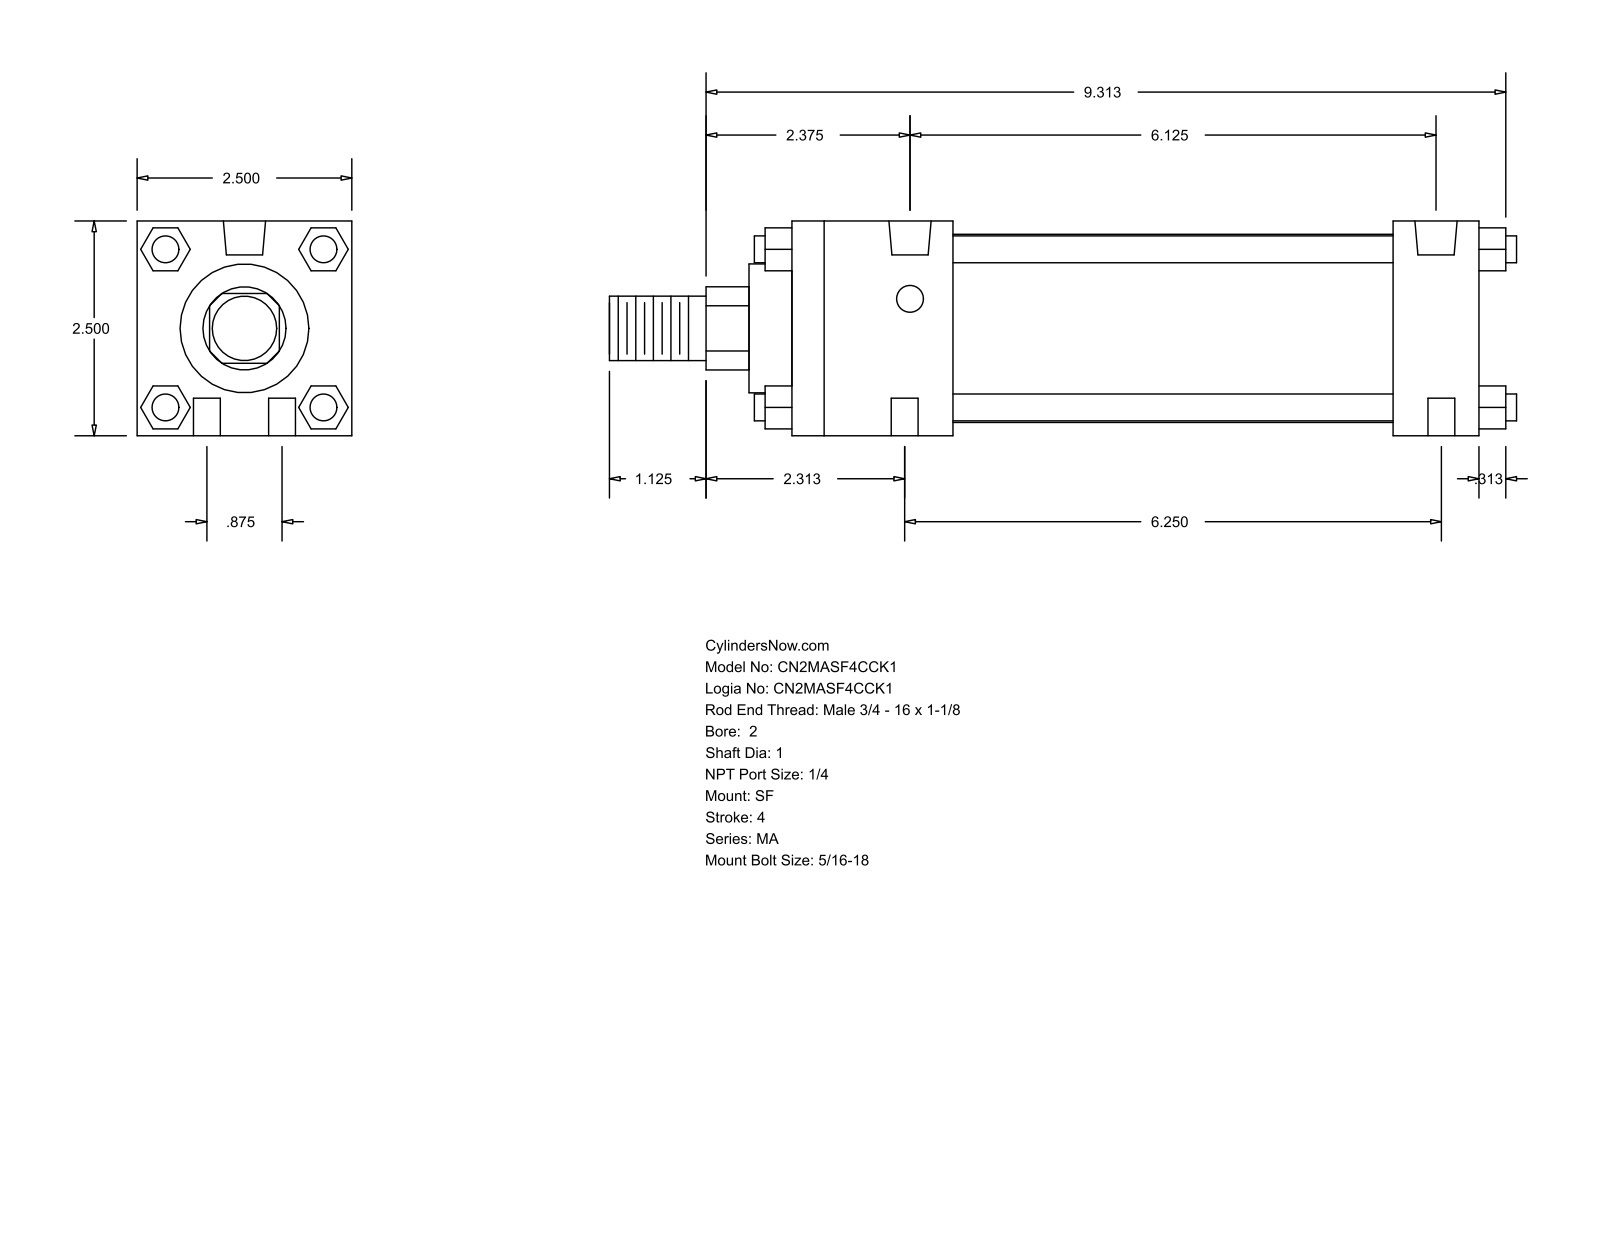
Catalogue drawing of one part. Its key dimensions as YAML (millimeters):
part_name: "MA_SF__0200_1"
step_written_by: "GSSL Pune (CONFIG_CONTROL_DESIGN)"
units: millimeters
bodies: {solids: 0, faces: 124, planar: 94, cylindrical: 30, other: 0}
overall_size: [268.29, 63.5, 63.5]
round_holes:
  - {diameter: 7.94, count: 6}
  - {diameter: 12.49, count: 2}
round_bosses_or_shafts:
  - {diameter: 7.94, count: 4}
  - {diameter: 55.63, count: 1}
  - {diameter: 38.1, count: 1}
  - {diameter: 25.4, count: 1}
  - {diameter: 19.05, count: 1}
partial_cylinders:
  - {radius: 12.29, count: 1}
face_to_face_distances: [63.5, 203.2, 12.7, 25.4, 177.8, 47.63, 130.17, 155.57, 40.47, 23.37]
hole_center_spacings: [11.22, 157.55, 22.22, 155.57, 158.75, 160.3]
